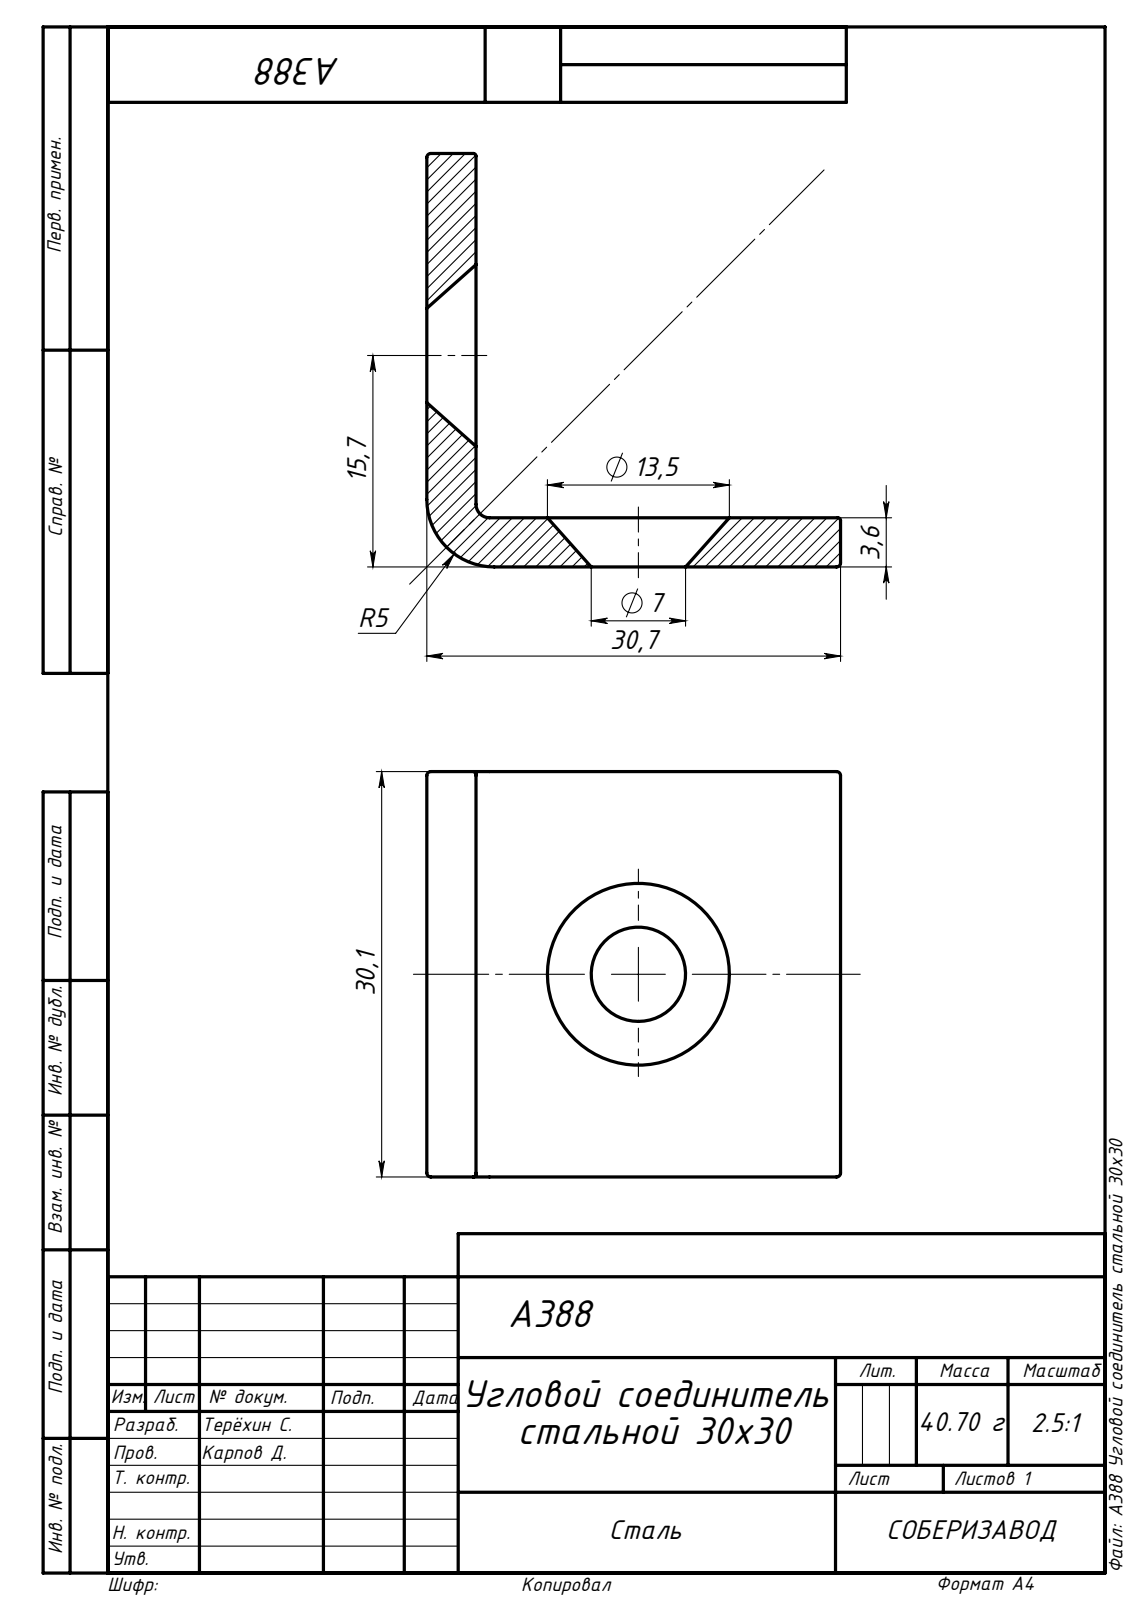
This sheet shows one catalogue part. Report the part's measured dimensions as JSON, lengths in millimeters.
{"part_name": "A388 Угловой соединитель стальной 30х30", "step_written_by": "SolidWorks 2020 (AUTOMOTIVE_DESIGN)", "units": "millimeters", "bodies": {"solids": 1, "faces": 42, "planar": 8, "cylindrical": 18, "other": 16}, "overall_size": [30.7, 30.7, 30.1], "volume_mm3": 5562, "surface_area_mm2": 3942, "partial_cylinders_radius": [[0.3, 10], [0.2, 6], [1, 1], [5, 1]], "face_to_face_distances": [3.65, 30.7, 27.05, 30.1]}
